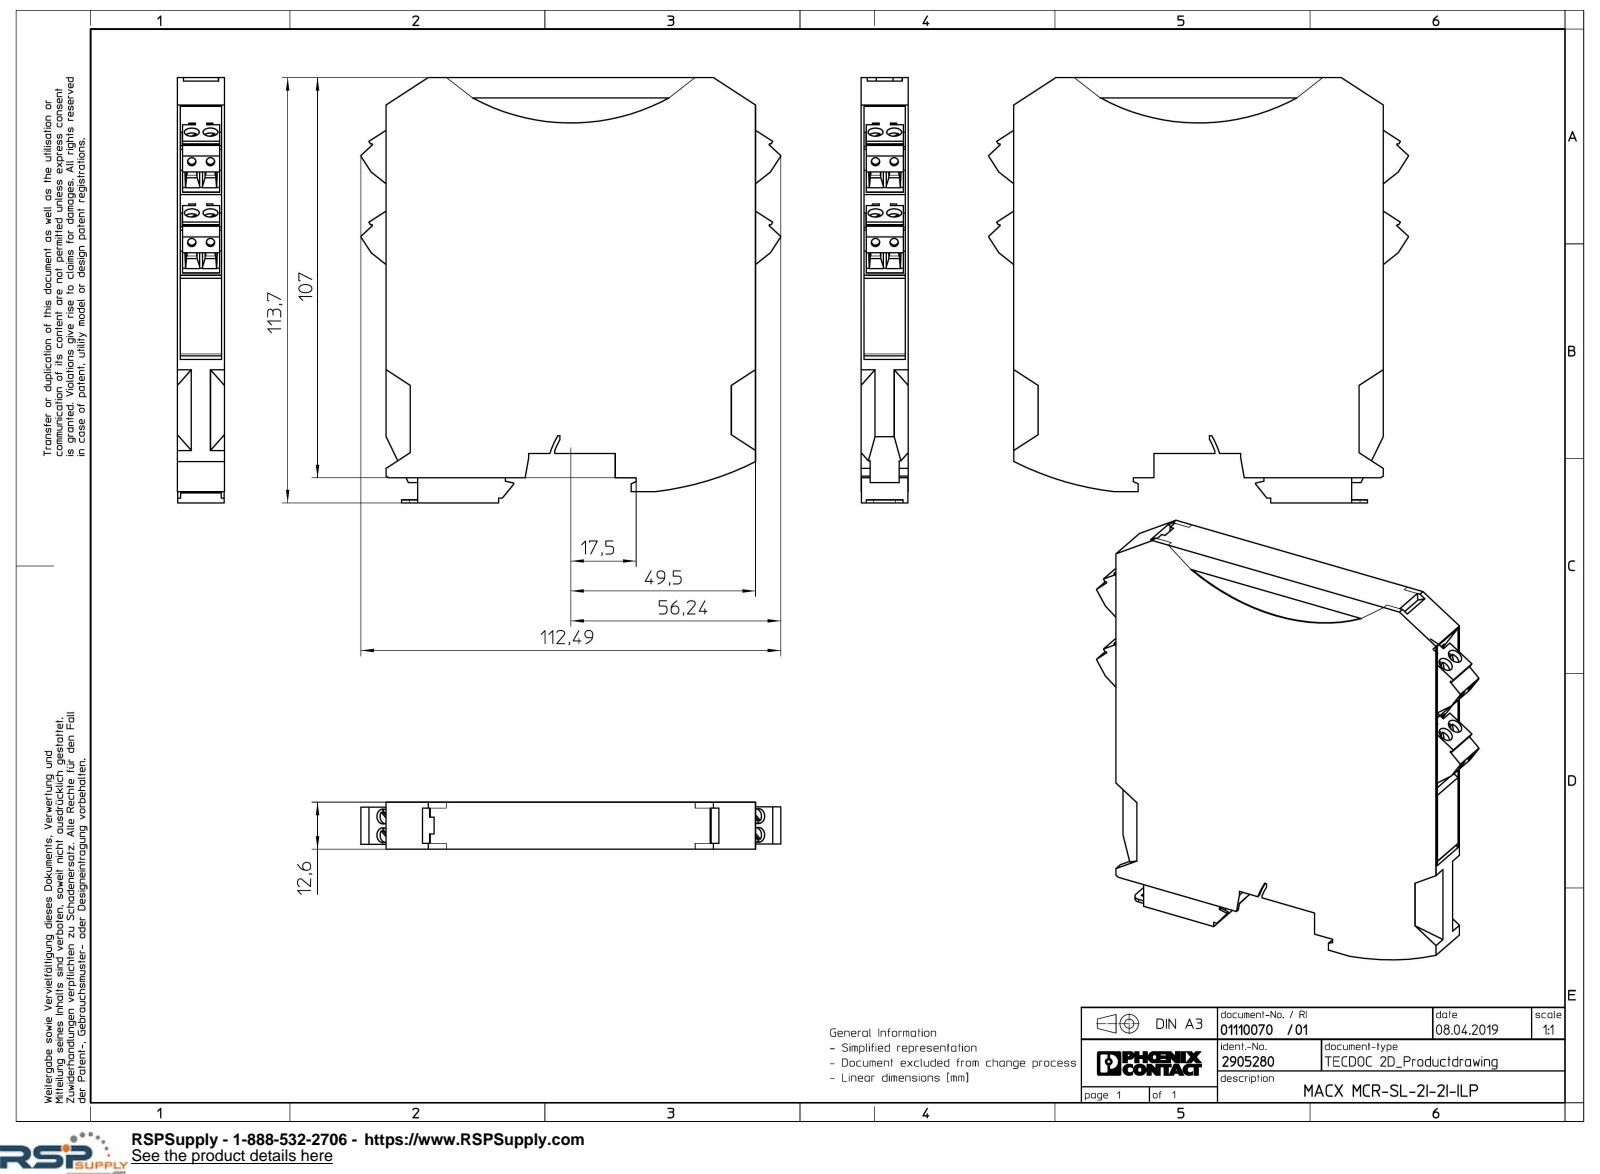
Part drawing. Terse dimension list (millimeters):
name: MACX_12.5_NO-TBUS-SOCKEL-select; ME_MAX_B-12.5_GN-select; MSTBTP_2.5_2-ST-select.1.1; MACX_MCR_12.5_150_1-select
written by: Creo Elements/Direct Modeling 20.1A 29-Sep-2018 (C) Parametric Technology GmbH (AUTOMOTIVE_DESIGN)
unit: mm
bodies: 7 solids, 890 faces (737 planar, 153 cylindrical, 0 other)
size: 113.7 × 112.73 × 12.6
volume: 125 908 mm³; area: 41 103 mm²
holes: 8× ⌀1.53, 8× ⌀2.23, 8× ⌀3, 8× ⌀4
bosses: 6× ⌀2.8
rounds: 18× R2, 14× R3, 8× R2.9, 8× R3.4, 6× R1.4, 4× R0.2, 4× R0.5, 2× R1.25
face distances: 12.6, 0.75, 11.85, 18.12, 11.8, 11.75, 11.1, 9.95, 11.77, 12.4
hole spacings: 5, 11.76, 11.77, 12.78, 12.79, 18.11, 18.12, 18.78
